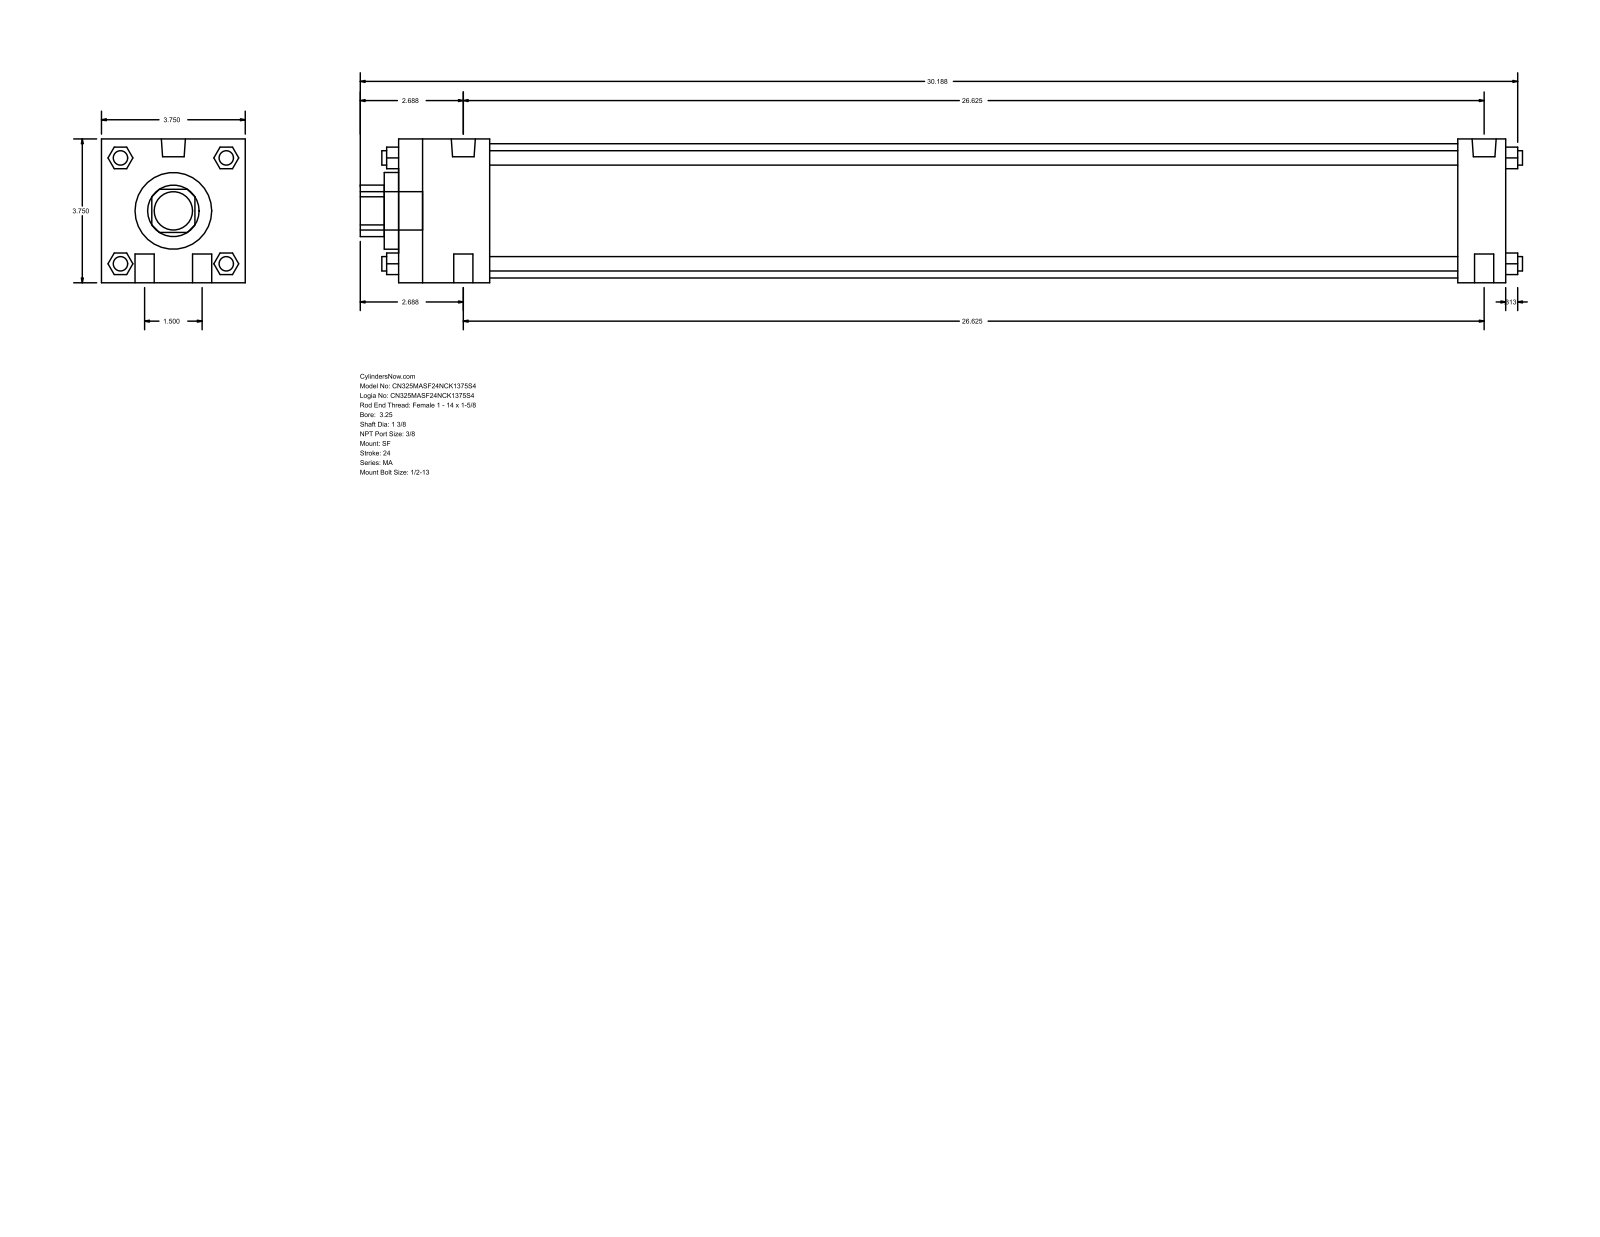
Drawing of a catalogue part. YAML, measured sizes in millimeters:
part_name: "MA_SF__0325_1.375"
step_written_by: "GSSL Pune (CONFIG_CONTROL_DESIGN)"
units: millimeters
bodies: {solids: 0, faces: 124, planar: 94, cylindrical: 30, other: 0}
overall_size: [769.94, 95.25, 95.25]
round_holes:
  - {diameter: 34.92, count: 1}
  - {diameter: 50.8, count: 1}
  - {diameter: 88.9, count: 1}
round_bosses_or_shafts:
  - {diameter: 12.7, count: 4}
  - {diameter: 9.53, count: 4}
  - {diameter: 15.93, count: 2}
  - {diameter: 11.11, count: 2}
  - {diameter: 25.4, count: 1}
partial_cylinders:
  - {radius: 17.06, count: 1}
face_to_face_distances: [95.24, 733.43, 701.68, 31.75, 60.32, 641.36, 673.11, 9.52, 69.84, 711.2]
